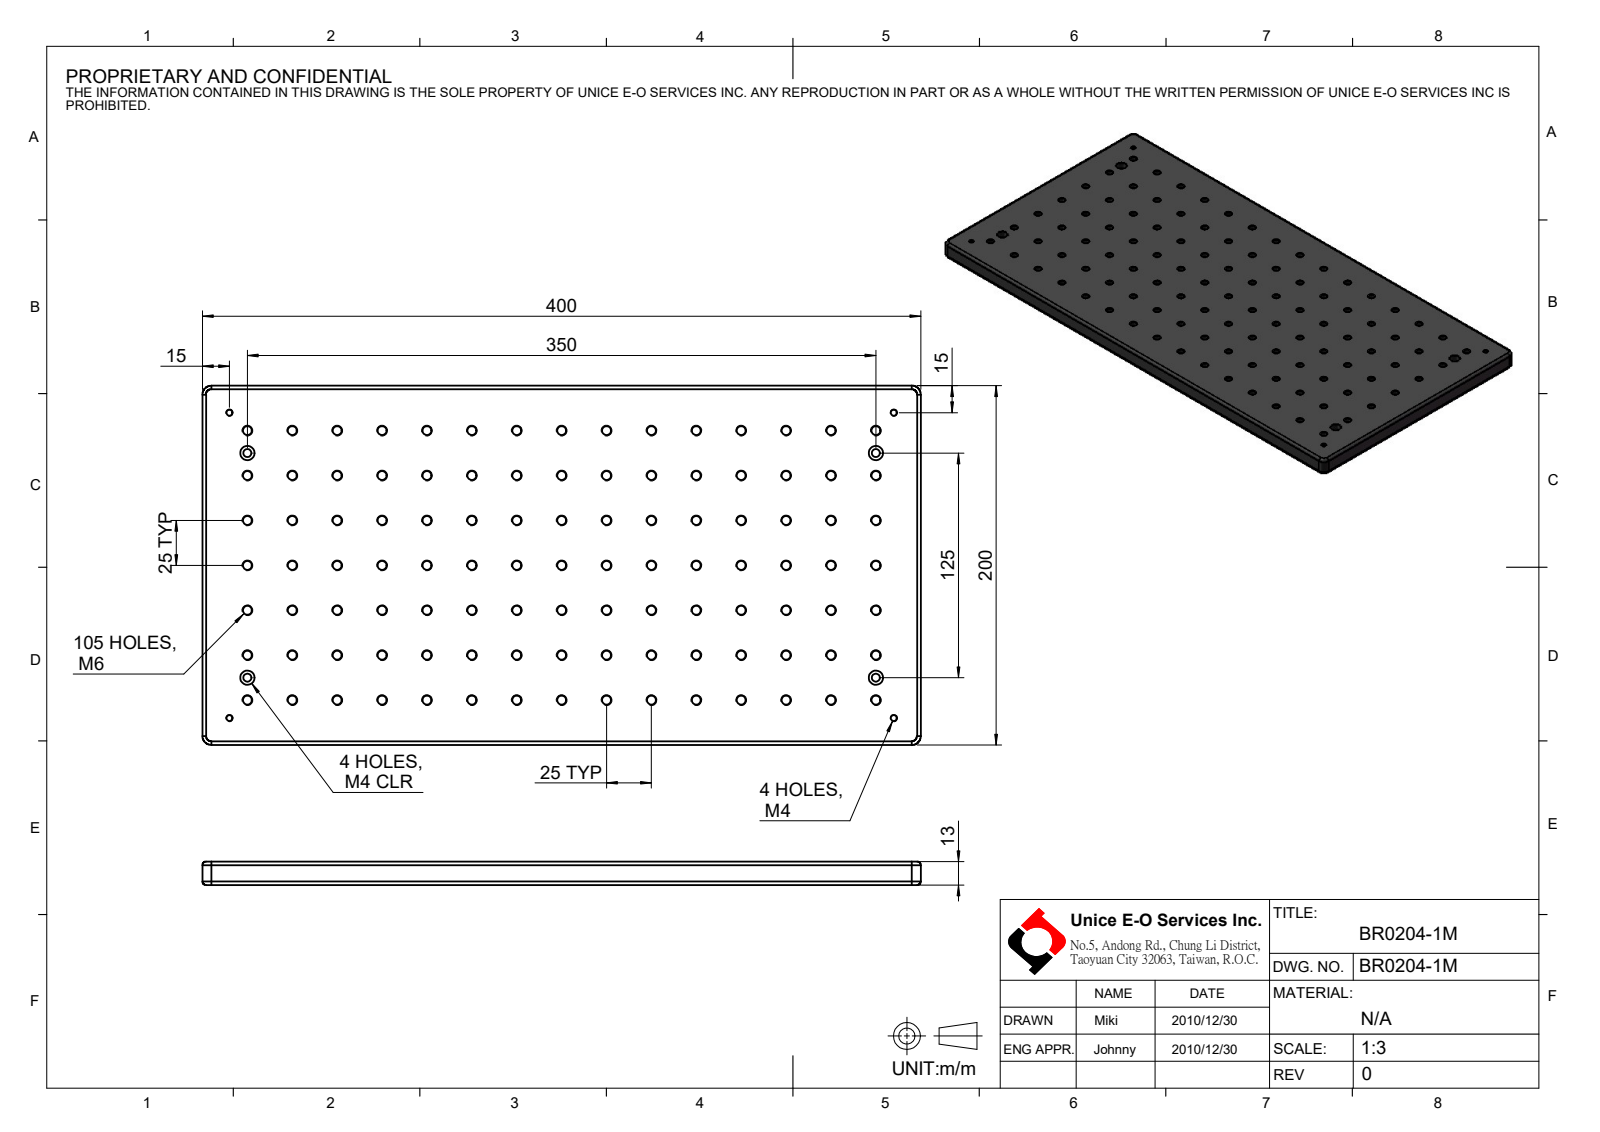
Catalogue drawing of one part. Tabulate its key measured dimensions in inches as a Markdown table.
| quantity | value |
| --- | --- |
| part name | BR0204-1M |
| STEP written by | SolidWorks 2016 (CONFIG_CONTROL_DESIGN) |
| units | inches |
| bodies | 1 solid, 264 faces (10 planar, 246 cylindrical, 8 other) |
| overall size | 15.748 × 7.874 × 0.512 |
| volume | 61.57 in³ |
| surface area | 297.7 in² |
| round holes (diameter × count) | 0.197 × 105, 0.13 × 4, 0.177 × 4, 0.315 × 4 |
| partial cylindrical surfaces (radius × count) | 0.079 × 8, 0.197 × 4 |
| main face-to-face distances | 0.512, 7.874, 15.748, 0.276, 0.236 |
| hole center spacings | 0.984, 1.969, 5.987, 2.953, 4.921, 6.225, 5.906, 6.603 |
